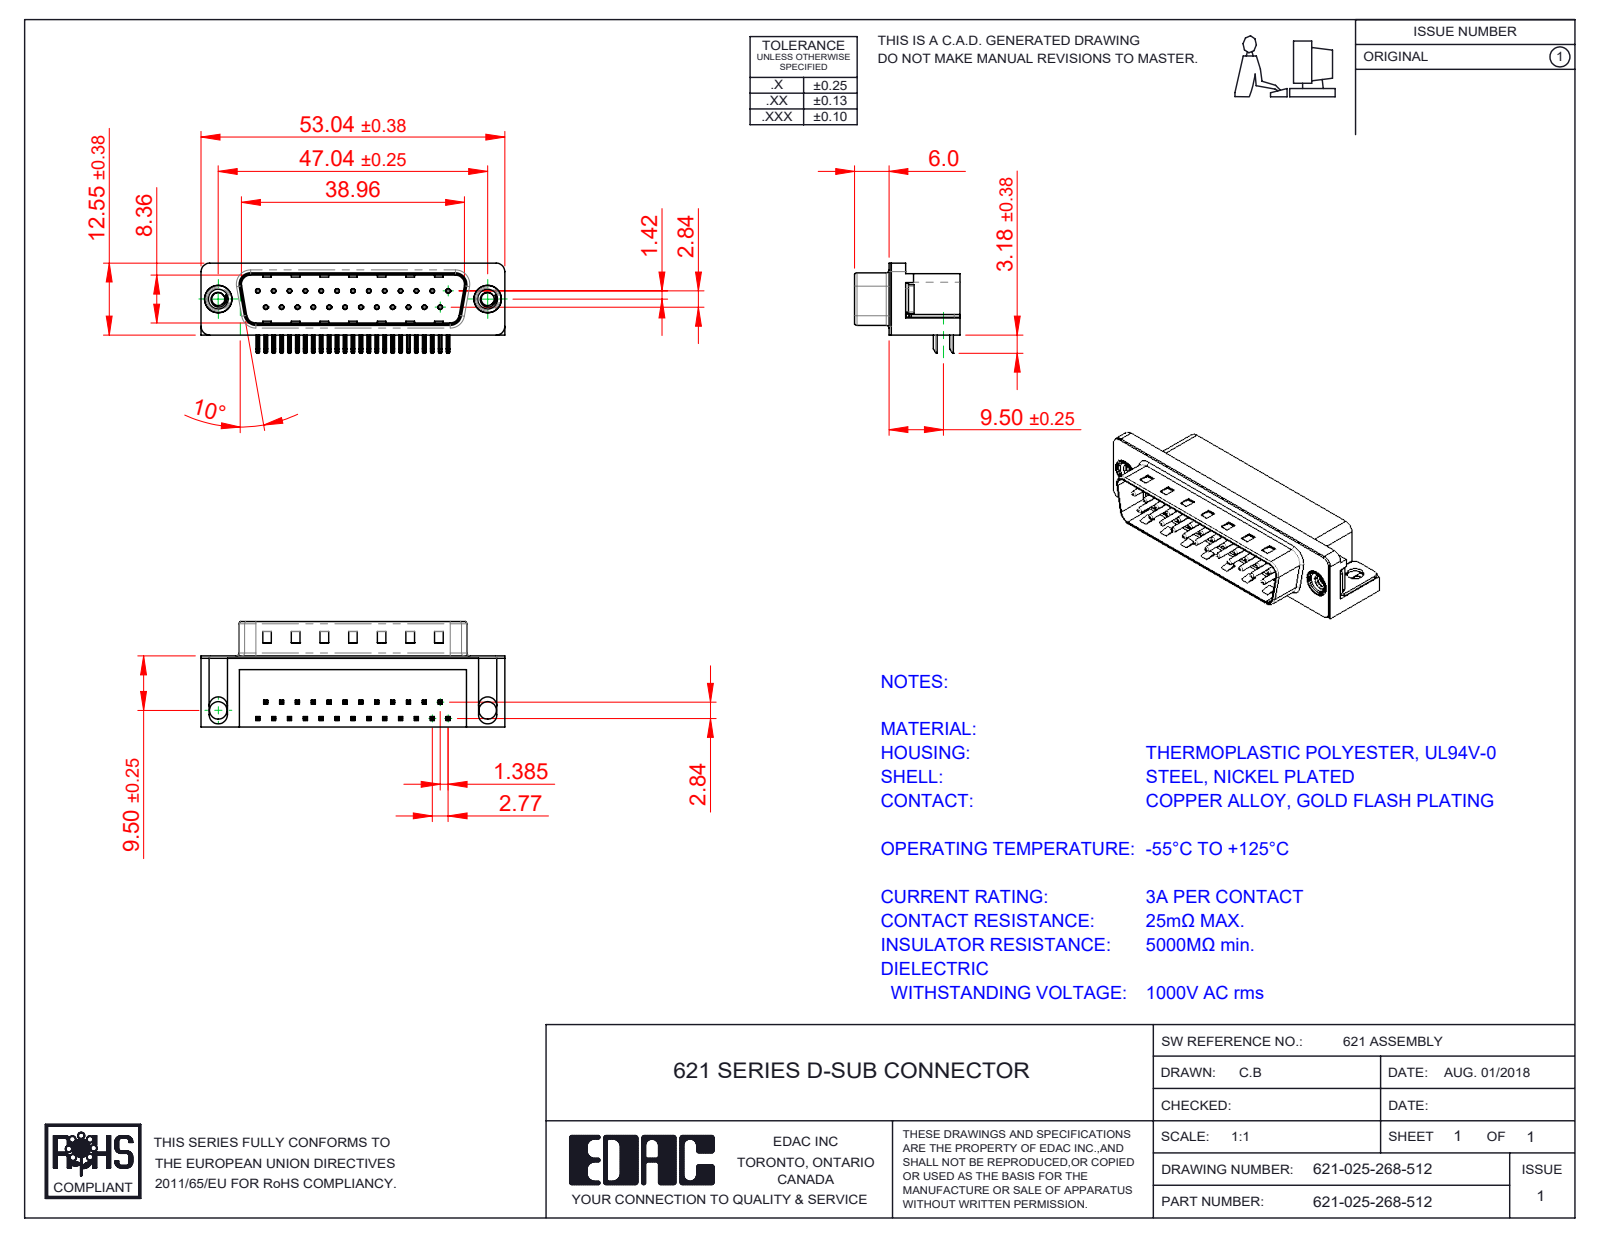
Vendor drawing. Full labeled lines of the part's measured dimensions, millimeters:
Part name (STEP PRODUCT): 621 Contact Bottom; 621-025-268-512; 621 Housing_25 Socket; 621 4-40 Threaded Rivet (+3 more)
STEP written by: SolidWorks 2016 (CONFIG_CONTROL_DESIGN)
Units: millimetres
Bodies: 31 solids, 2261 faces (1403 planar, 659 cylindrical, 199 other)
Overall size (bounding box): 53.04 × 18.4 × 15.73
Volume: 6 347 mm³ · Surface area: 7 670 mm²
Round holes (diameter × count): ⌀0.35 ×25, ⌀0.8 ×25, ⌀2.26 ×2, ⌀3.05 ×2, ⌀4 ×2, ⌀4.8 ×2, ⌀5 ×2
Round bosses / shafts (diameter × count): ⌀0.75 ×25, ⌀4.9 ×2, ⌀4.75 ×2, ⌀3.9 ×2
Partial cylindrical surfaces — rounded edges, fillets, slot ends (radius × count): R0.25 ×108, R0.12 ×50, R1 ×16, R0.5 ×9, R1.6 ×8, R1.5 ×7, R0.9 ×4, R2 ×4
Main face-to-face distances: 0.4, 12, 10.35, 2.1, 8.76, 10.46, 1.7, 10.86, 12.4, 9
Hole centre spacings: 3.16, 2.77, 5.54, 8.31, 11.08, 13.85, 16.62, 5.03
